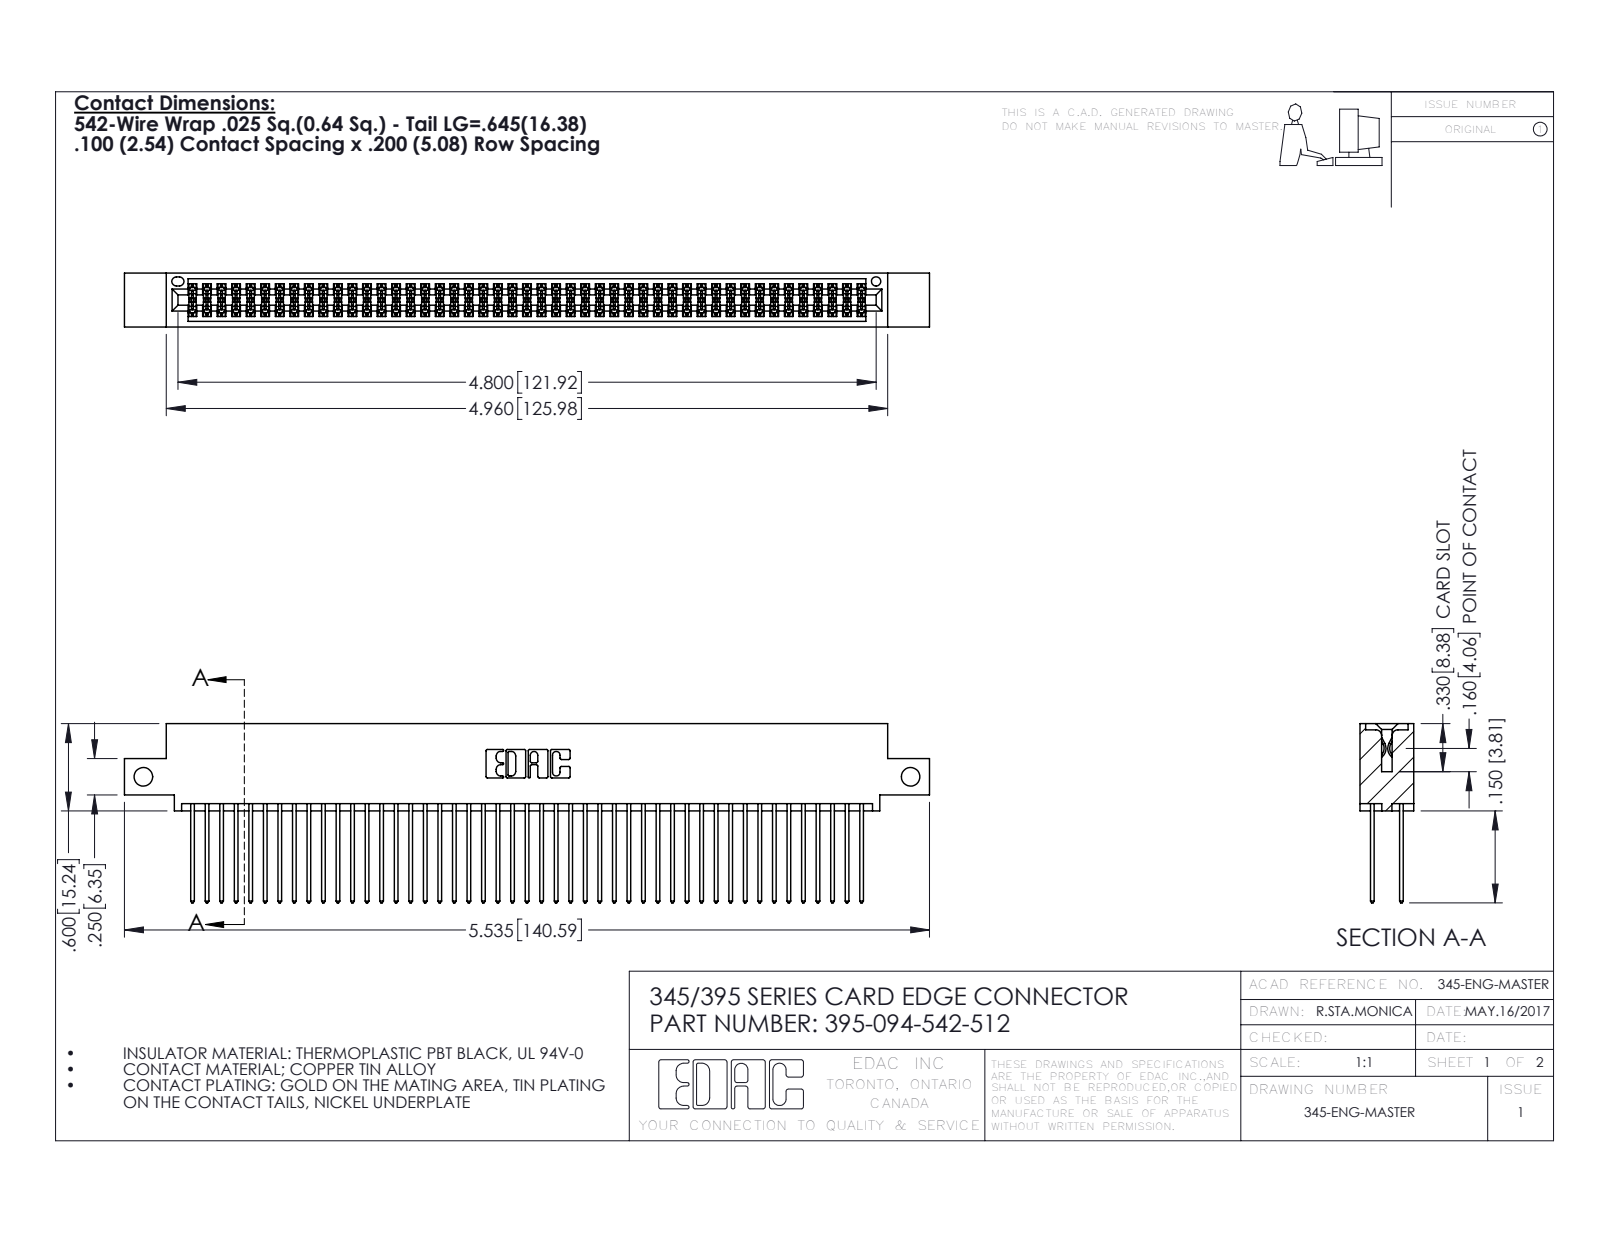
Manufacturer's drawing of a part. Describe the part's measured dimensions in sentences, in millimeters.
The part is named "345-292-001_345-293-142; 395-094-542-512; 345 Part_0.110 Offset - Side Mount". Its 3-D file was written by "SolidWorks 2016 (CONFIG_CONTROL_DESIGN)". It is 95 solids with 4830 faces: 3186 planar, 1644 cylindrical and 0 other. Overall it measures 140.6 by 31.3 by 9.4 millimeters. Its volume is 14 000 cubic millimeters and its surface area 22 770 square millimeters. Round holes: 2 of diameter 3.3, 1 of diameter 1.6. Partial cylindrical surfaces (rounded edges, fillets, slot ends): 141 of radius 0.2, 94 of radius 0.3, 22 of radius 0.3, 6 of radius 0.2, 6 of radius 0.8, 3 of radius 0.7, 2 of radius 0.4, 2 of radius 0.5. The main face-to-face distances are 7.6, 1.8, 5.1, 2.5, 6.9, 0.6, 5.7, 9.4, 4.4, 3.8. The hole center spacings are 134.
